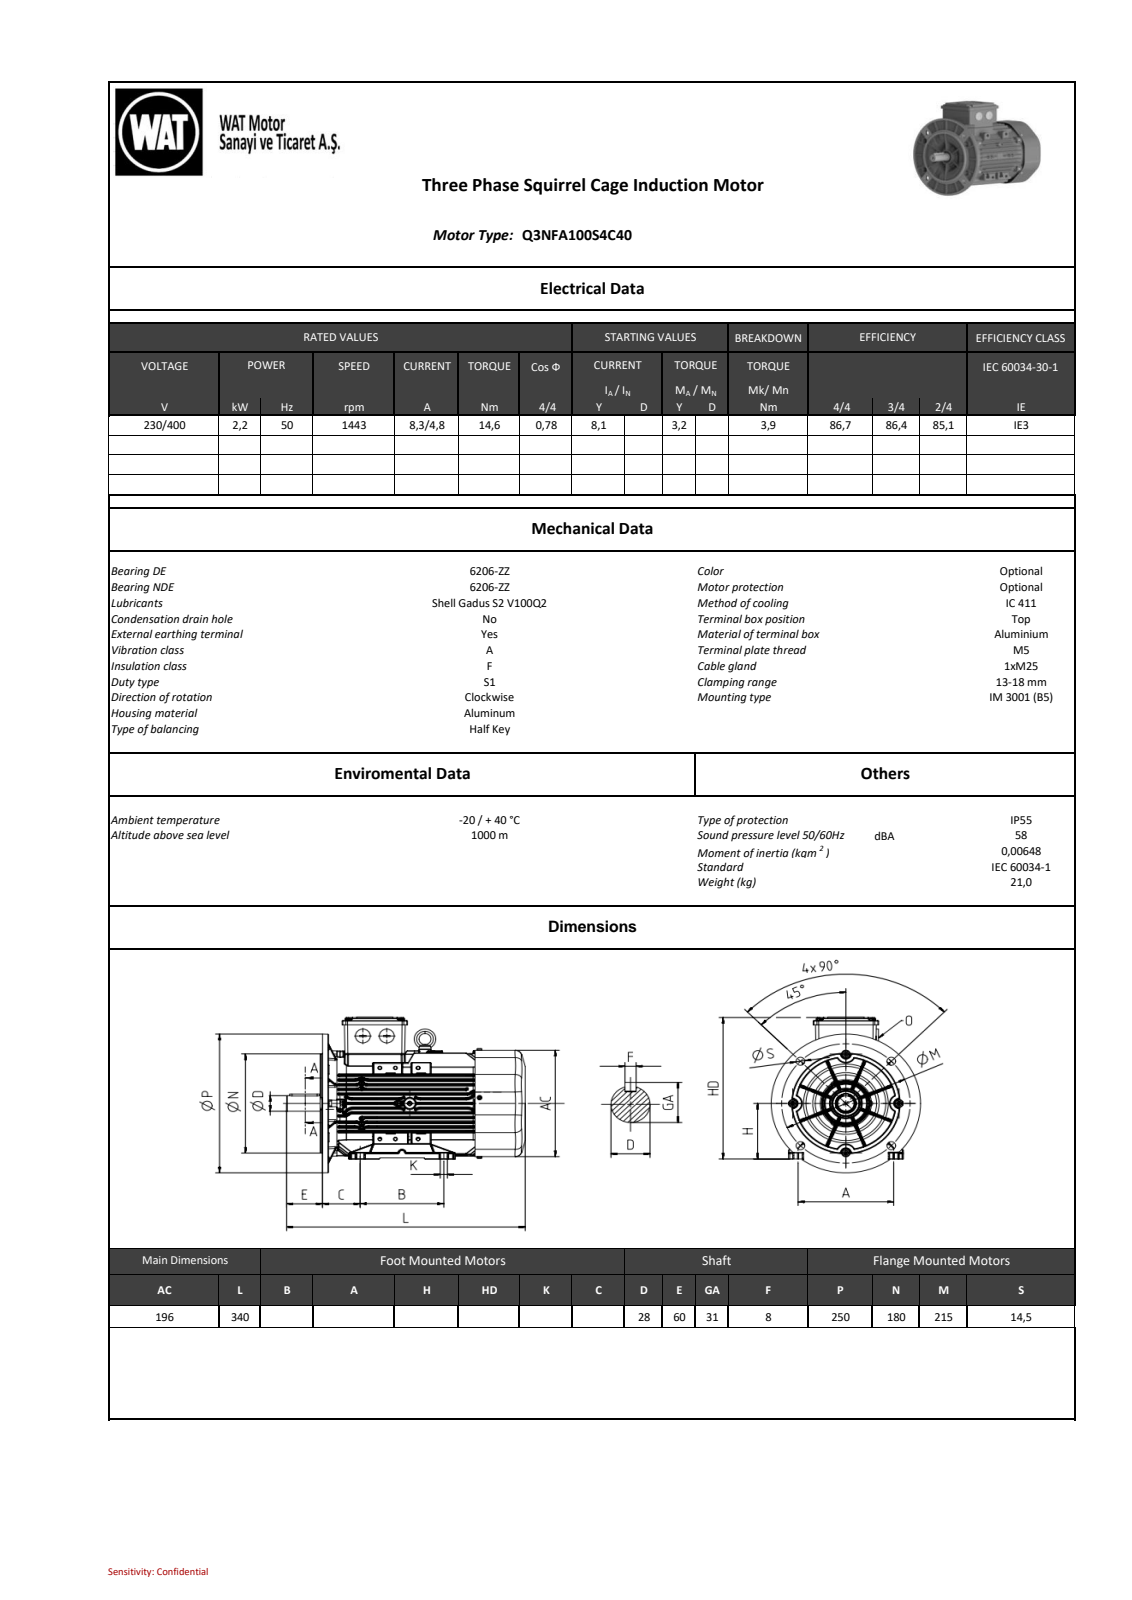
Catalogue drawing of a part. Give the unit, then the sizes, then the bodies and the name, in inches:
Units: inches
Overall size (bounding box): 13.386 × 10.038 × 9.8
Round holes (diameter × count): ⌀0.197 ×6, ⌀0.256 ×6, ⌀0.079 ×2, ⌀0.098 ×2, ⌀0.118 ×2, ⌀0.472 ×2, ⌀0.984 ×2, ⌀0.157 ×1, ⌀0.335 ×1, ⌀0.413 ×1, ⌀1.126 ×1, ⌀1.297 ×1
Round bosses / shafts (diameter × count): ⌀0.315 ×7, ⌀0.157 ×7, ⌀0.465 ×6, ⌀0.394 ×6, ⌀0.236 ×6, ⌀1.378 ×2, ⌀1.094 ×2, ⌀0.994 ×2
Partial cylindrical surfaces — rounded edges, fillets, slot ends (radius × count): R0.02 ×1761, R0.03 ×610, R0.031 ×446, R0.039 ×208, R0.01 ×144, R0.059 ×132, R0.157 ×99, R0.079 ×67
Main face-to-face distances: 0.031, 0.236, 0.079, 0.52, 0.283, 1.614, 9.409, 0.551, 10.472, 10.756
Hole centre spacings: 3.622, 1.535, 3.785, 6.177, 7.244, 0.478, 0.556, 0.672
Bodies: 0 solids, 15765 faces (3330 planar, 5345 cylindrical, 7090 other)
Part name (STEP PRODUCT): C90127E0127Fj6t7
STEP written by: SIEMENS PLM Software NX 11.0 (AUTOMOTIVE_DESIGN)
